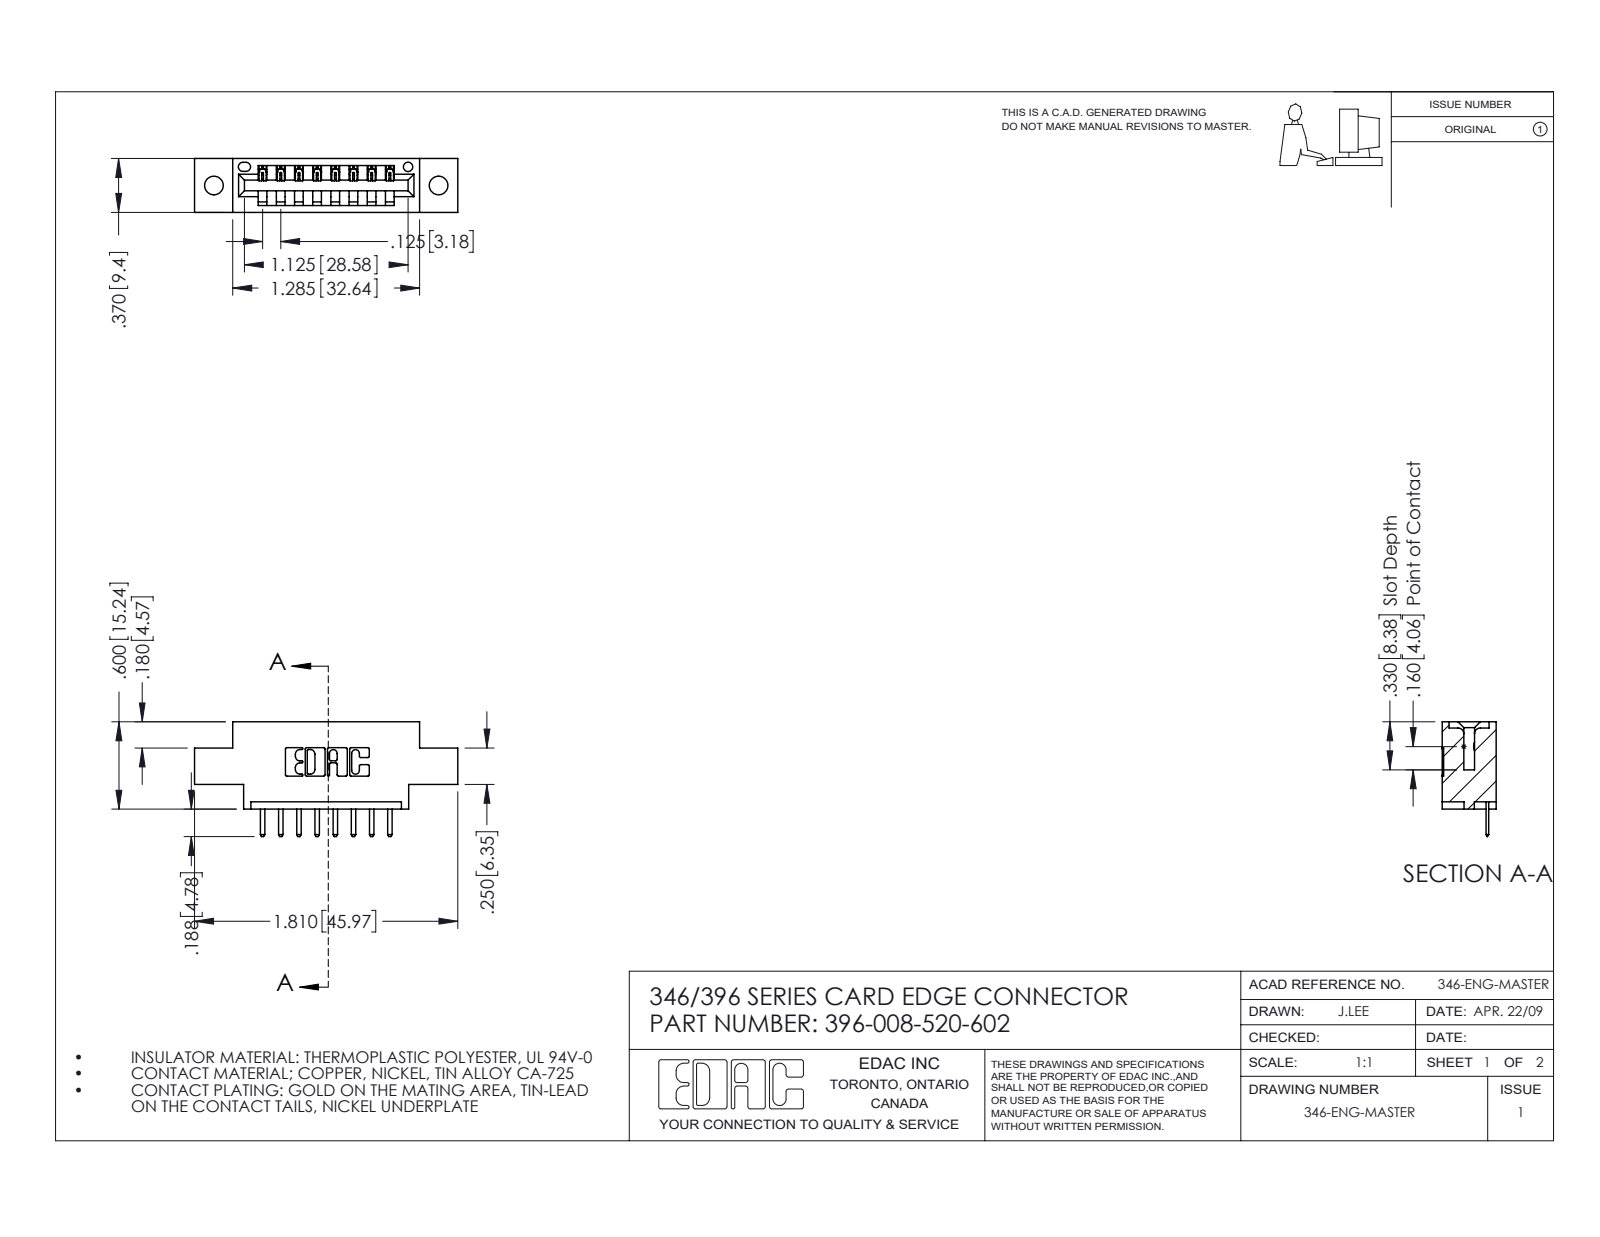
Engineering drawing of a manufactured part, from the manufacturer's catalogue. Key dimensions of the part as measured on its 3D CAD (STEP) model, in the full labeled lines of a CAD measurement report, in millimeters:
Part name (STEP PRODUCT): 345-292-001_345-293-120; 396-008-520-602; 346 Part_0.170 Offset - 0.128 Dia
STEP written by: SolidWorks 2016 (CONFIG_CONTROL_DESIGN)
Units: millimetres
Bodies: 9 solids, 622 faces (416 planar, 206 cylindrical, 0 other)
Overall size (bounding box): 46 × 20 × 9.4
Volume: 3 950 mm³ · Surface area: 4 385 mm²
Round holes (diameter × count): ⌀3.3 ×2, ⌀1.6 ×1
Partial cylindrical surfaces — rounded edges, fillets, slot ends (radius × count): R0.3 ×22, R0.3 ×18, R0.2 ×16, R0.2 ×6, R0.8 ×6, R0.7 ×3, R0.8 ×2, R1 ×2
Main face-to-face distances: 6.4, 9.4, 1.2, 8.2, 3.8, 5.6, 2.5, 4.4, 12.7, 4.7
Hole centre spacings: 6.2, 34.1, 39.2
